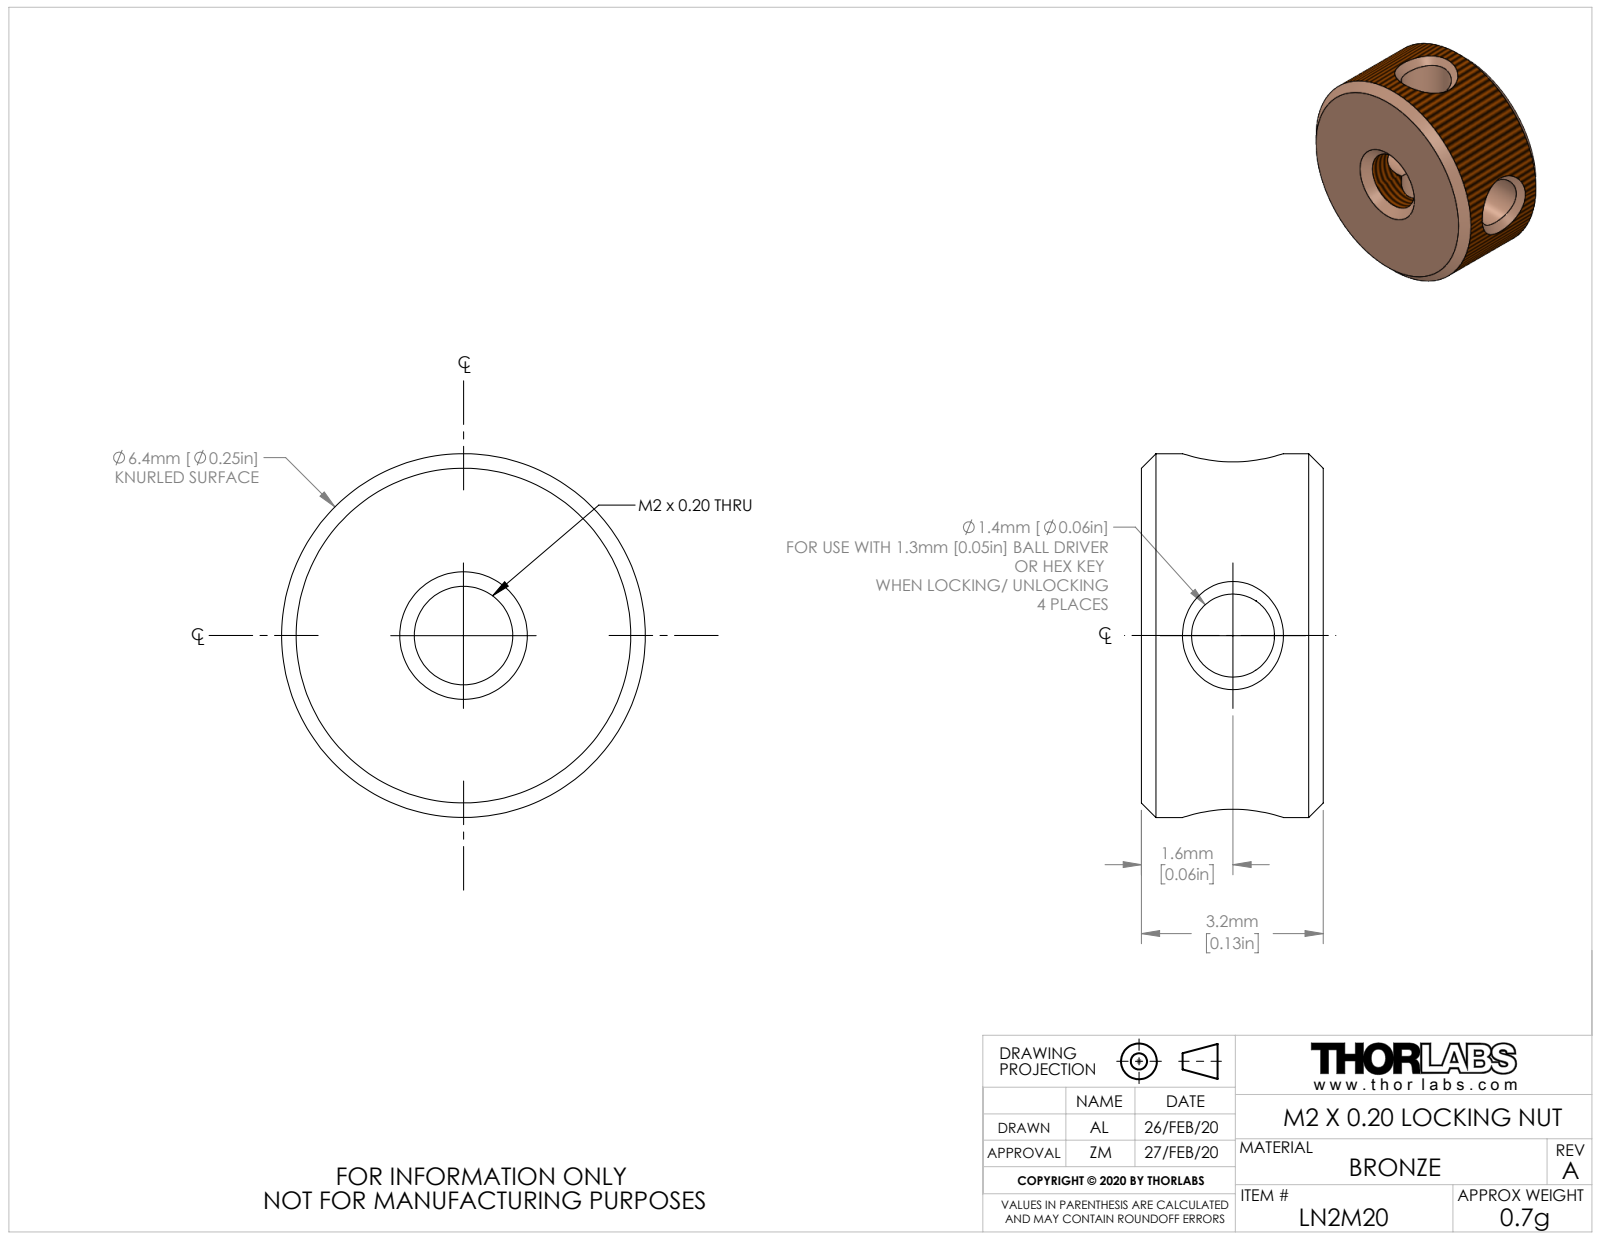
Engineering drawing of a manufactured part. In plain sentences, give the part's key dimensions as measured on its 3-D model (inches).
The part is named "TTN210099-E0W". Its 3-D file was written by "SolidWorks 2018 (AUTOMOTIVE_DESIGN)". It is 1 solid with 32 faces: 2 planar, 14 cylindrical and 16 other. Overall it measures 0.25 by 0.25 by 0.125 inches. Its volume is 0.005 cubic inches and its surface area 0.247 square inches. Round holes: 2 of diameter 0.057, 1 of diameter 0.068. Round bosses or shafts: 1 of diameter 0.25. The main face-to-face distances are 0.125.
